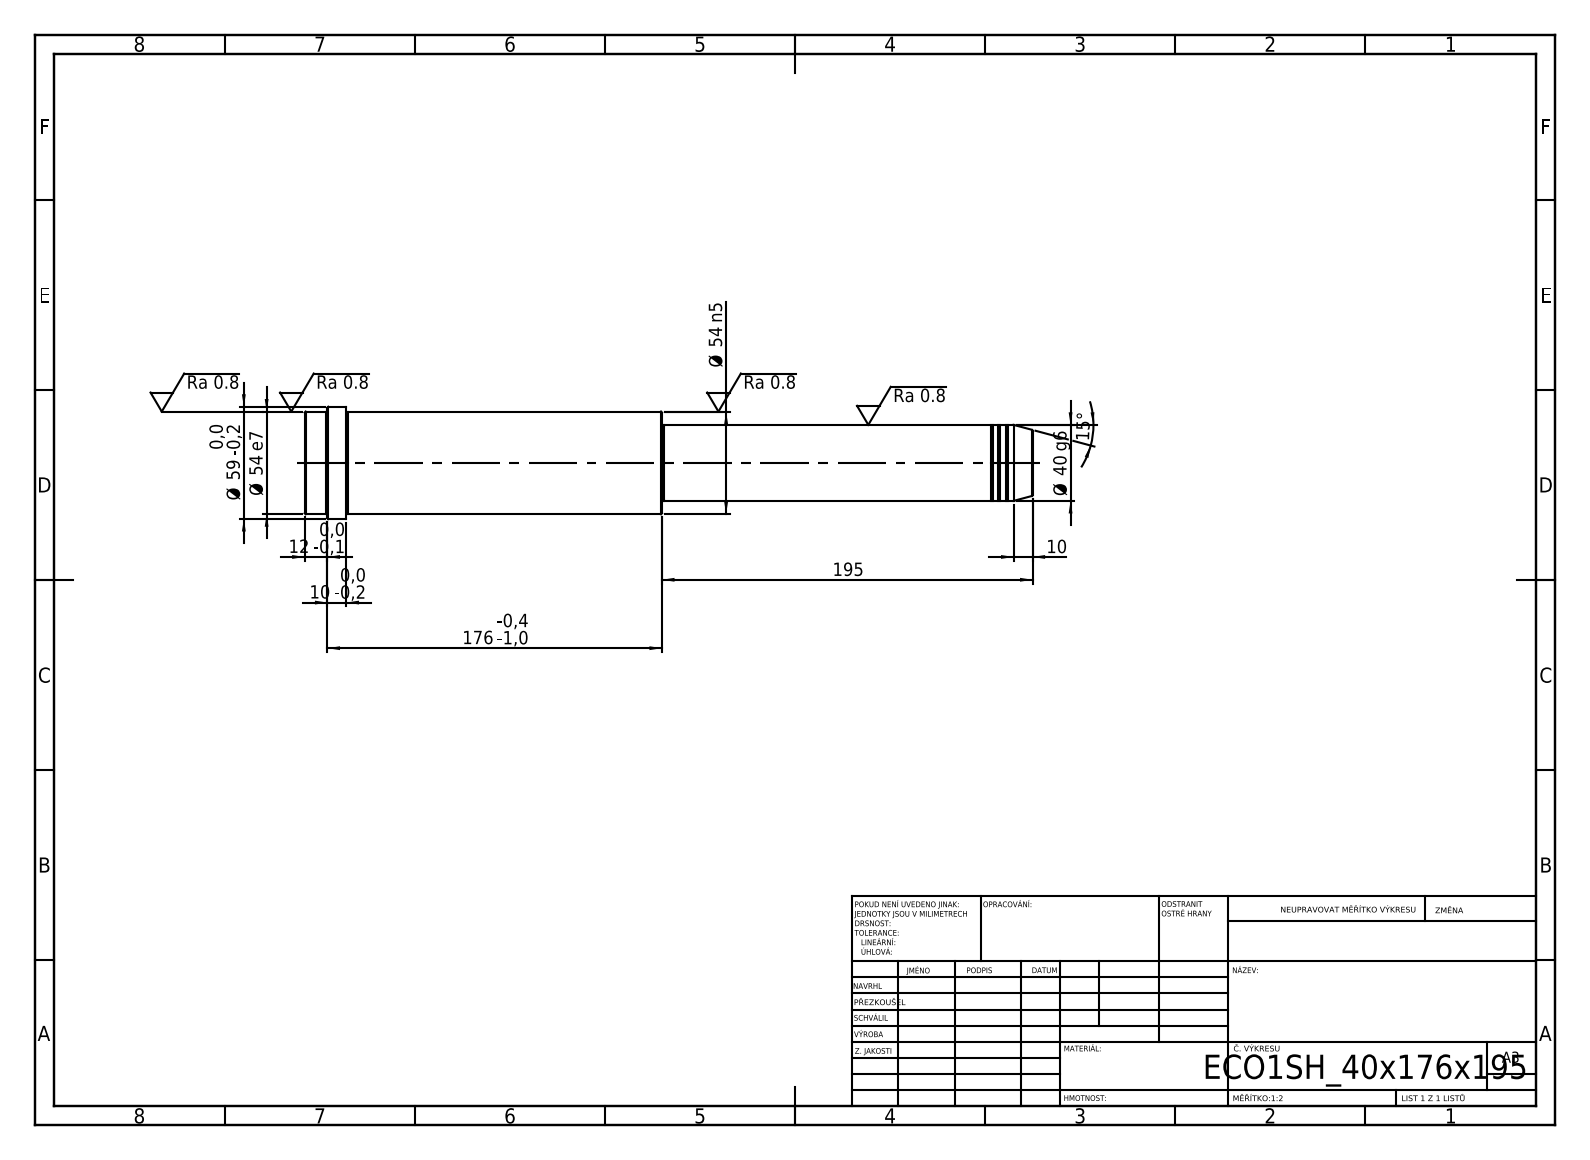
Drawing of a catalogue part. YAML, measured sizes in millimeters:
step_written_by: "SolidWorks 2019 (CONFIG_CONTROL_DESIGN)"
units: millimeters
bodies: {solids: 1, faces: 52, planar: 6, cylindrical: 16, other: 30}
overall_size: [383, 59, 59]
volume: 678026
surface_area: 62013
round_bosses_or_shafts:
  - {diameter: 59, count: 1}
  - {diameter: 54, count: 1}
  - {diameter: 40, count: 1}
  - {diameter: 39, count: 1}
face_to_face_distances: [188, 195, 383, 361, 166, 22, 371, 176, 10, 12]
